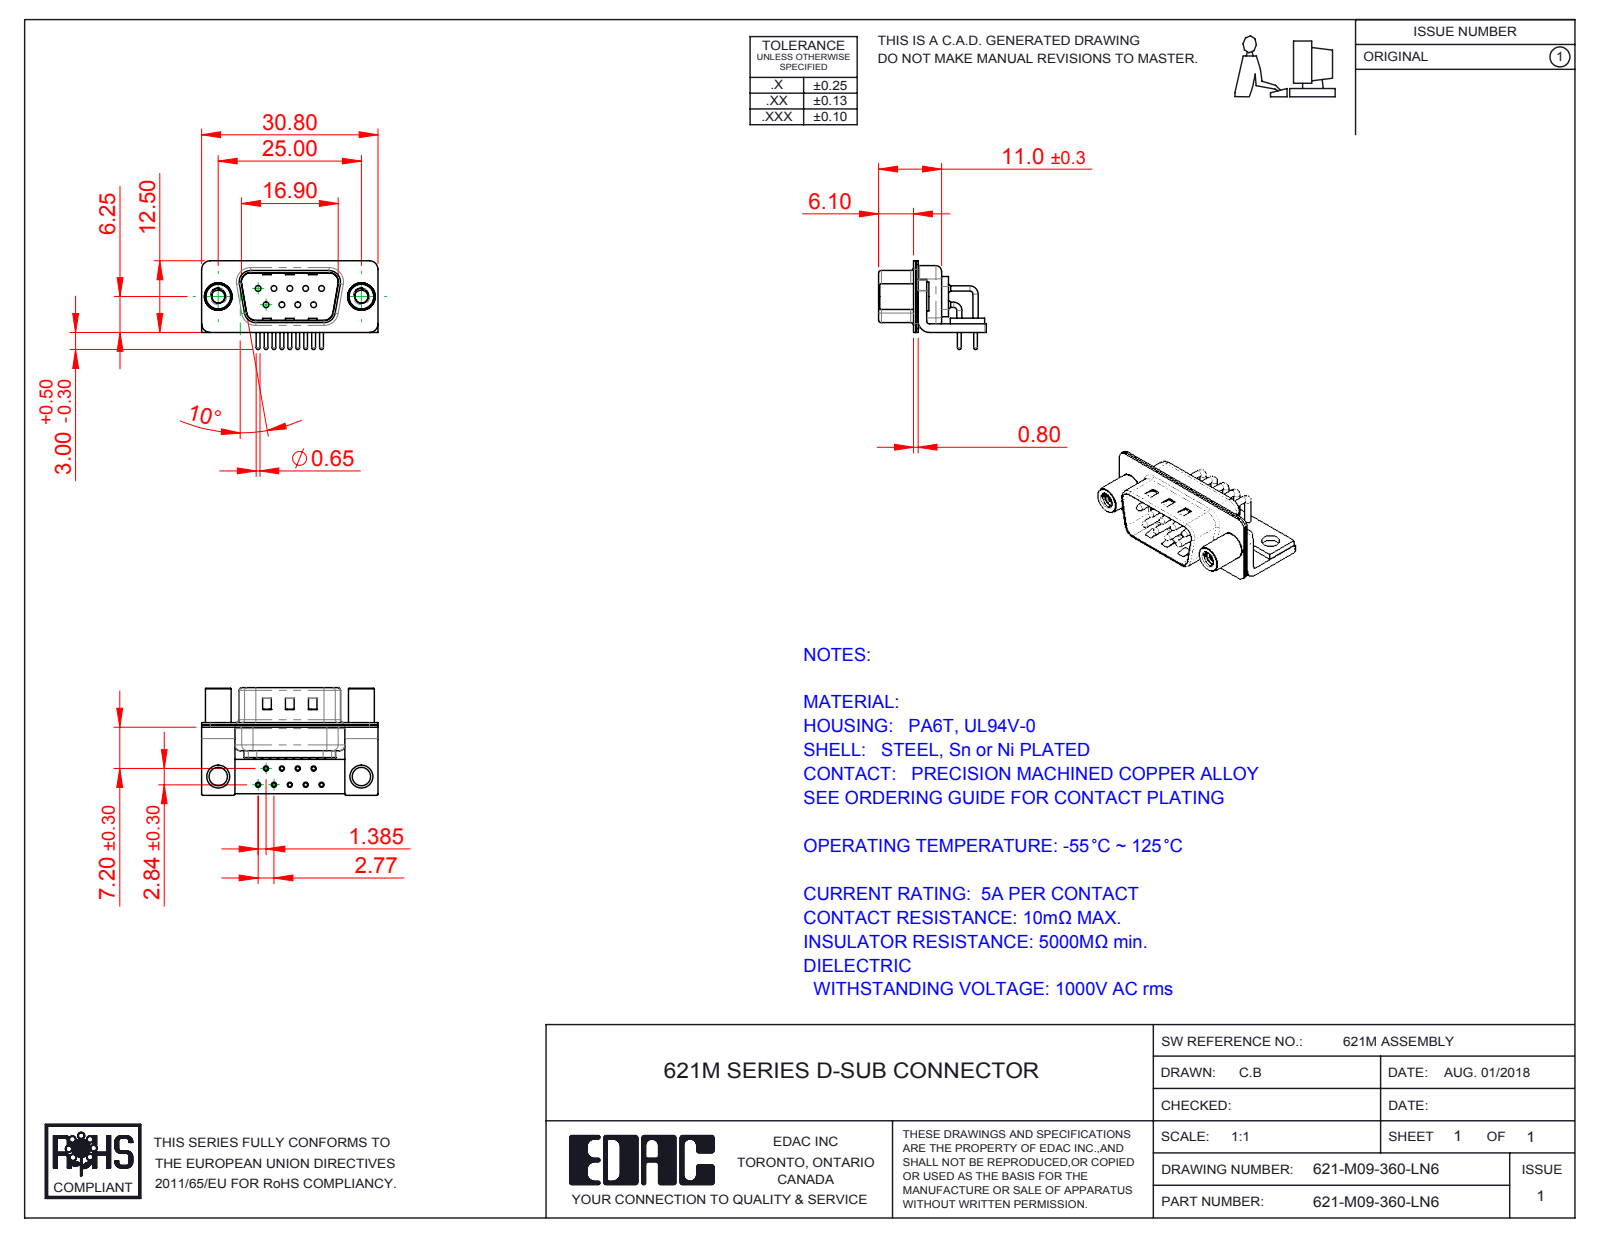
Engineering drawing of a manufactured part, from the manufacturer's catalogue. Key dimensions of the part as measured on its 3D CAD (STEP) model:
Part name (STEP PRODUCT): 621M Stabilizer Bracket; 621M Contact Row 2; 621M Contact Row 1; 621M Shell Rear_09 Contacts (+5 more)
STEP written by: SolidWorks 2016 (CONFIG_CONTROL_DESIGN)
Units: millimetres
Bodies: 17 solids, 1412 faces (711 planar, 535 cylindrical, 166 other)
Overall size (bounding box): 30.8 × 18.8 × 15.49
Volume: 1 882 mm³ · Surface area: 5 133 mm²
Round holes (diameter × count): ⌀0.9 ×9, ⌀1 ×9, ⌀1.7 ×9, ⌀2 ×9, ⌀2.26 ×2, ⌀3.2 ×2, ⌀4 ×2, ⌀4.8 ×2
Round bosses / shafts (diameter × count): ⌀1.5 ×9, ⌀0.9 ×9, ⌀0.65 ×9, ⌀5 ×2, ⌀4.9 ×2, ⌀4.5 ×2
Partial cylindrical surfaces — rounded edges, fillets, slot ends (radius × count): R0.25 ×16, R1.5 ×16, R2 ×13, R0.5 ×9, R1.01 ×9, R1.6 ×8, R0.6 ×4, R0.65 ×4
Main face-to-face distances: 0.4, 1.5, 0.8, 0.85, 1.25, 1.9, 1, 10.4, 9.55, 10.8
Hole centre spacings: 3.16, 2.77, 5.54, 5.03, 5.04, 8.31, 7.48, 7.49
